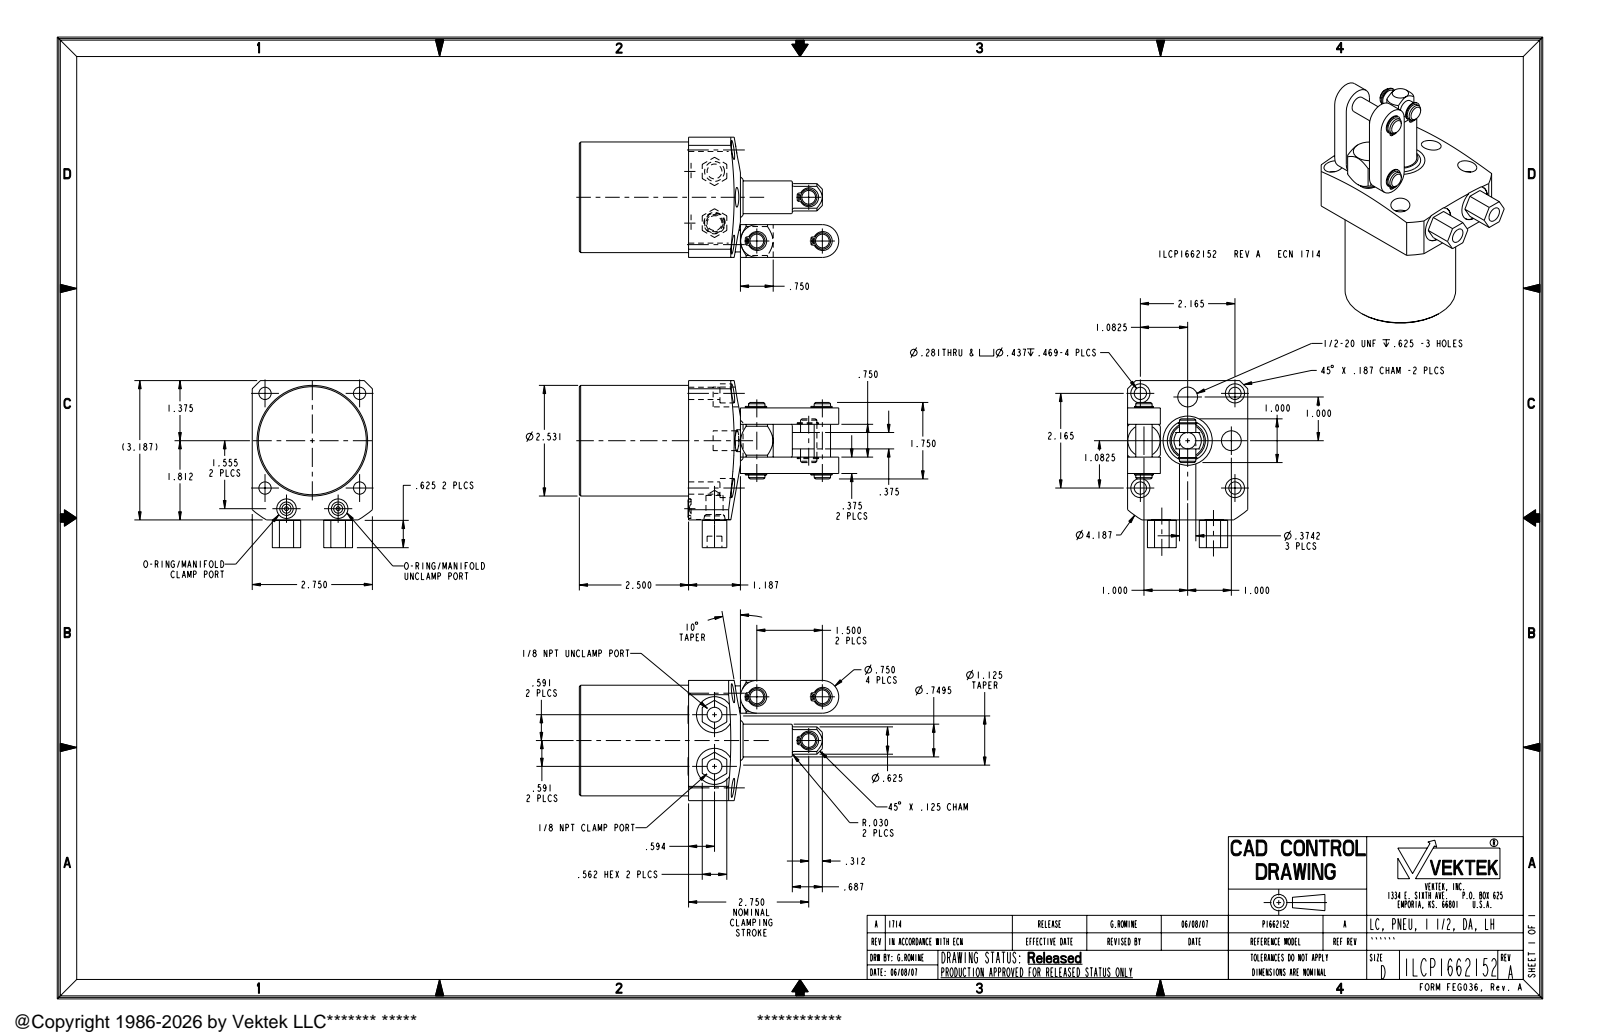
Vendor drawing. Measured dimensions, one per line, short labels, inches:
name: ILCP1662152
written by: PRO/ENGINEER BY PARAMETRIC TECHNOLOGY CORPORATION, 2005180 (AUTOMOTIVE_DESIGN_CC2)
unit: in
bodies: 3 solids, 298 faces (120 planar, 130 cylindrical, 48 other)
size: 5.937 × 3.822 × 2.75
volume: 24.02 in³; area: 78.33 in²
holes: 6× ⌀0.041, 4× ⌀0.281, 4× ⌀0.437, 2× ⌀0.339, 2× ⌀0.392, 2× ⌀0.447, 2× ⌀0.453, 2× ⌀0.825
bosses: 3× ⌀0.433, 3× ⌀0.374, 2× ⌀0.437, 1× ⌀2.531, 1× ⌀0.75, 1× ⌀0.5
rounds: 12× R0.041, 2× R0.375, 1× R0.313, 1× R0.5, 1× R2.094
face distances: 2.5, 2.75, 1.125, 0.375, 0.75, 0.625, 1.5, 2.125, 1.75, 0.562
hole spacings: 1.086, 2.165, 2.347, 0.098, 0.682, 1.048, 1.182, 1.5
